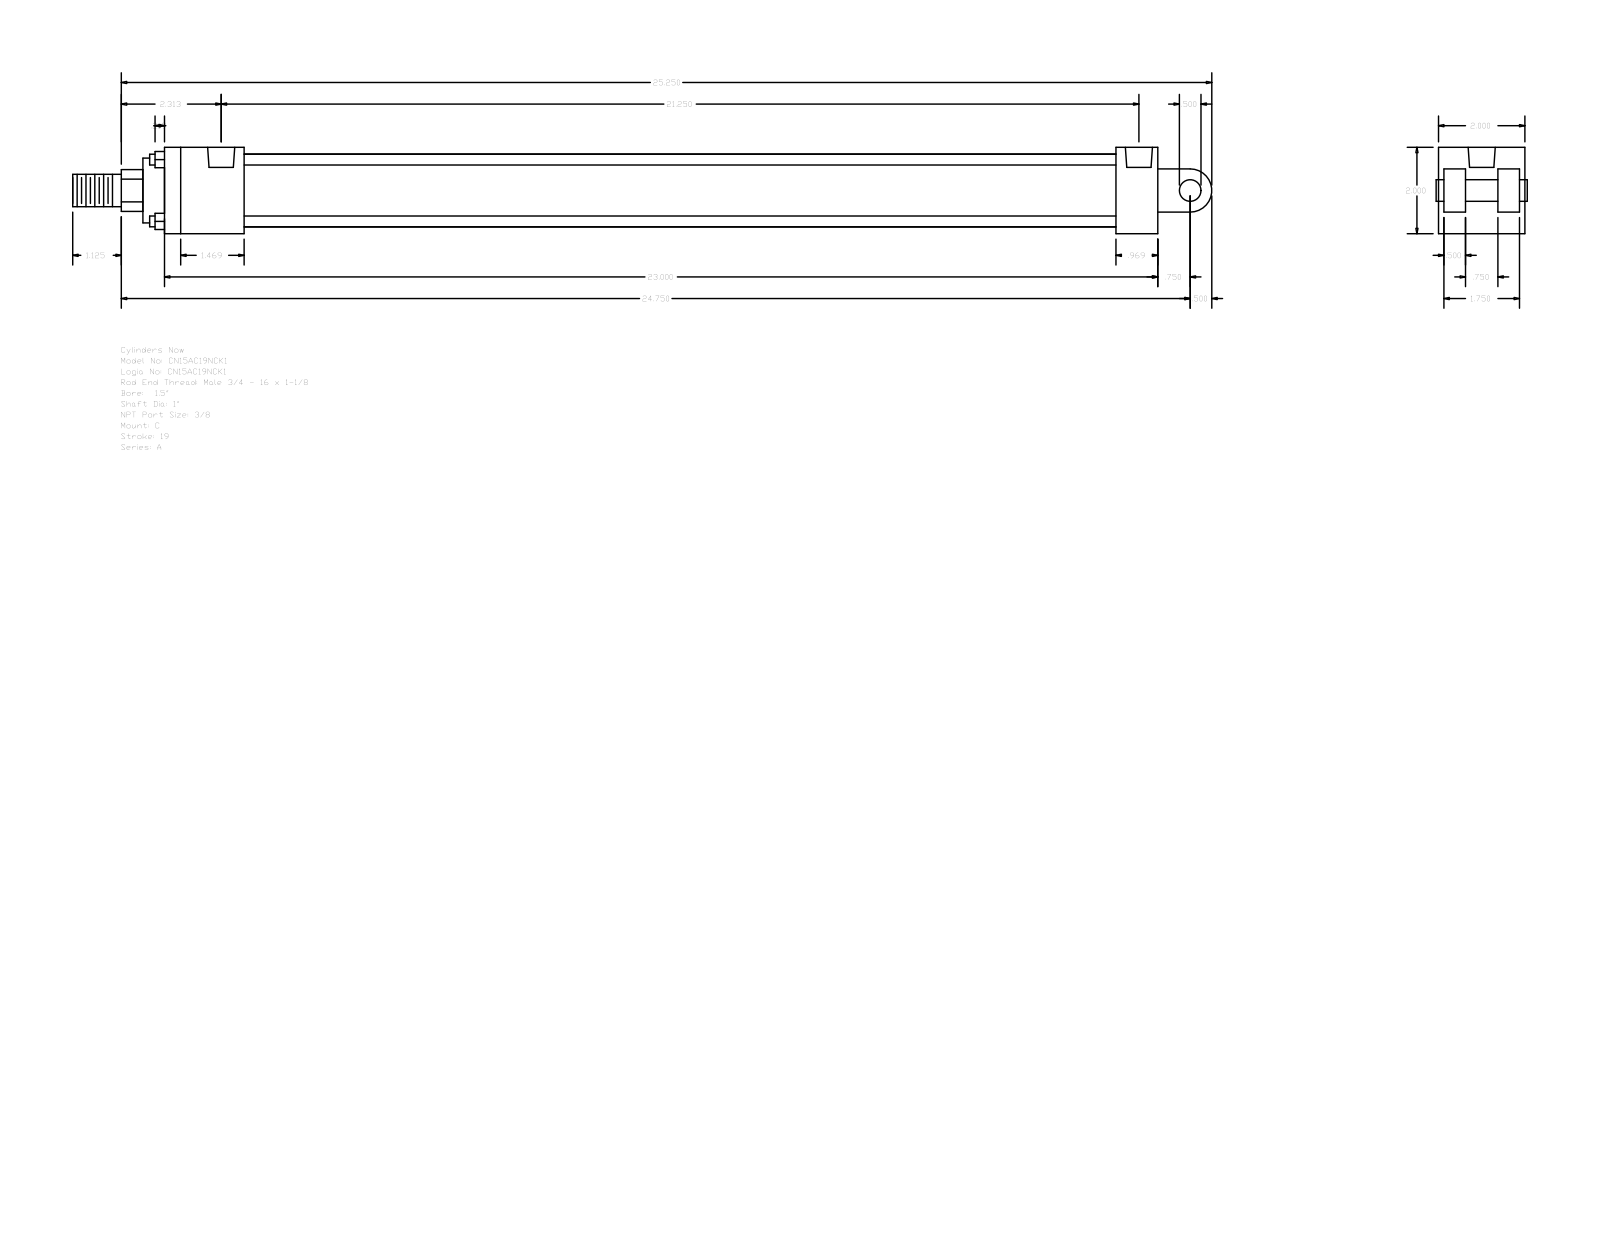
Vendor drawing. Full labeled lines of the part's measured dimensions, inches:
Part name (STEP PRODUCT): A_C__0150_1
STEP written by: GSSL Pune (CONFIG_CONTROL_DESIGN)
Units: inches
Bodies: 0 solids, 99 faces (70 planar, 29 cylindrical, 0 other)
Overall size (bounding box): 26.375 × 2 × 2
Round holes (diameter × count): ⌀0.219 ×4, ⌀0.627 ×2
Round bosses / shafts (diameter × count): ⌀0.25 ×4, ⌀1.69 ×1, ⌀1.5 ×1, ⌀1 ×1, ⌀0.75 ×1, ⌀0.5 ×1
Partial cylindrical surfaces — rounded edges, fillets, slot ends (radius × count): R0.484 ×1, R0.5 ×1
Main face-to-face distances: 2, 0.5, 0.125, 0.625, 1.875, 1.375, 1.25, 23, 1.5, 22.031
Hole centre spacings: 0.156, 20.937, 21.094, 21.25
